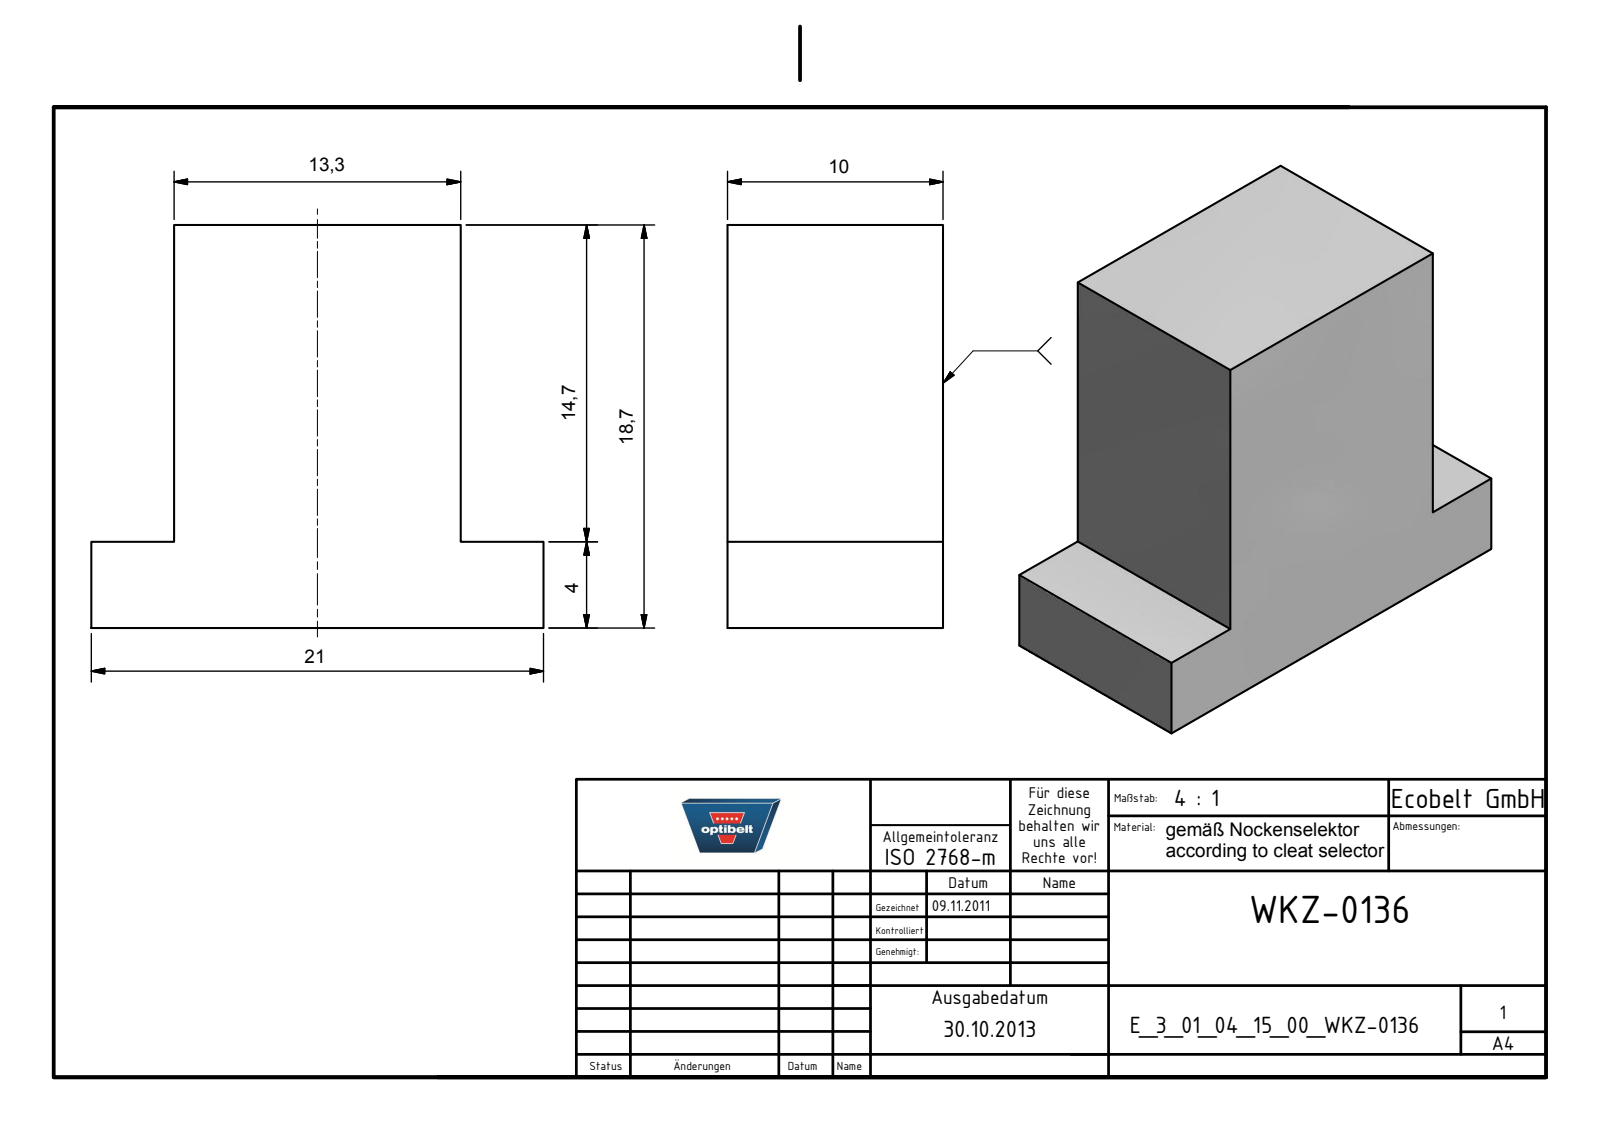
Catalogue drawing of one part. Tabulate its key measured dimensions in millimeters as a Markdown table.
| quantity | value |
| --- | --- |
| part name | E_3_01_04_15_00_WKZ-0136 |
| STEP written by | Autodesk Inventor 2025 (AUTOMOTIVE_DESIGN) |
| units | millimeters |
| bodies | 1 solid, 10 faces (10 planar, 0 cylindrical, 0 other) |
| overall size | 21 × 18.7 × 10 |
| volume | 2 795 mm³ |
| surface area | 1 353 mm² |
| main face-to-face distances | 10, 13.3, 18.7, 3.85, 17.15, 4, 14.7, 21 |
